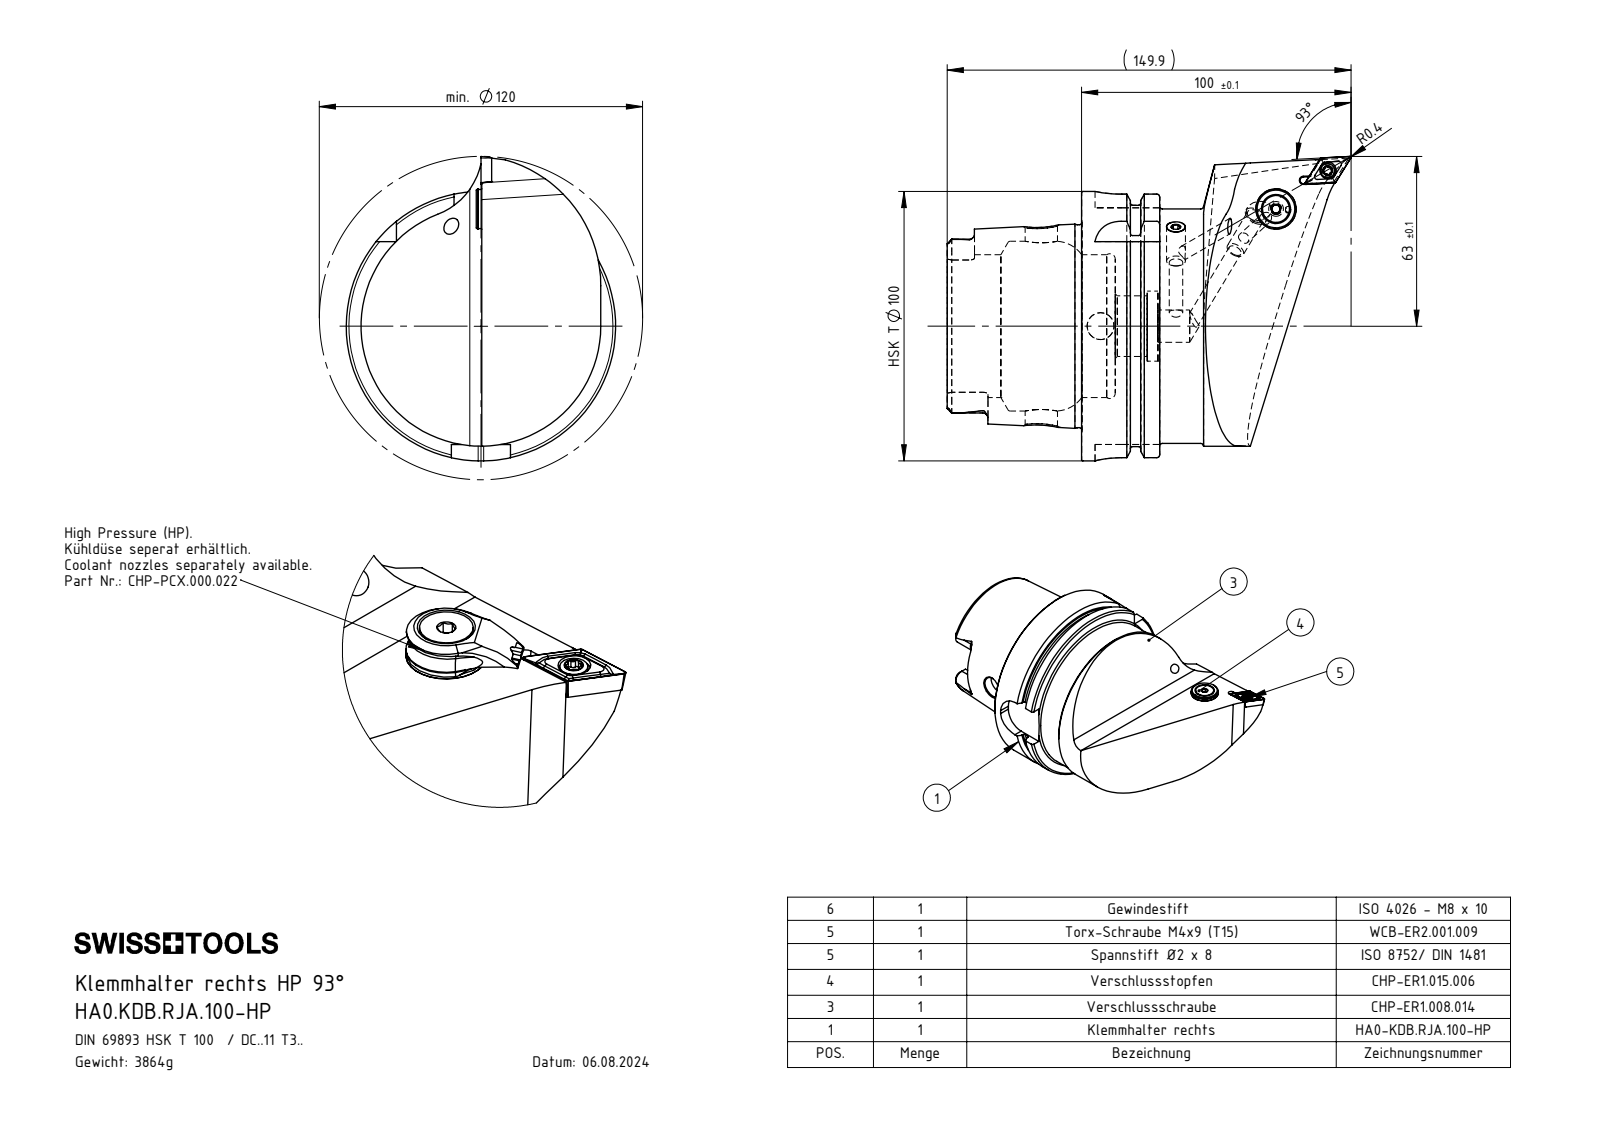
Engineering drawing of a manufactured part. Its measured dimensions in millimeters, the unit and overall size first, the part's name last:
Units: millimetres
Overall size (bounding box): 149.91 × 113 × 100
Round holes (diameter × count): ⌀5 ×3, ⌀4.2 ×2, ⌀12 ×2, ⌀1.2 ×1, ⌀2 ×1, ⌀2.5 ×1, ⌀3 ×1, ⌀3.3 ×1, ⌀4.4 ×1, ⌀5.2 ×1, ⌀6.1 ×1, ⌀6.8 ×1
Round bosses / shafts (diameter × count): ⌀8 ×2, ⌀100 ×1, ⌀91.95 ×1, ⌀87 ×1, ⌀75.26 ×1, ⌀15 ×1, ⌀13.4 ×1, ⌀10 ×1
Partial cylindrical surfaces — rounded edges, fillets, slot ends (radius × count): R0.34 ×6, R0.59 ×6, R1.9 ×6, R10 ×4, R4.83 ×2, R4.88 ×2, R1.25 ×1, R6 ×1
Main face-to-face distances: 12.45, 28.95, 16.5, 49.9, 62.35, 78.85, 87.8, 78.2, 28.3, 15.85
Hole centre spacings: 4.5, 20.7, 20.82, 23.9, 24.03, 78.34, 81.94, 102.22
Volume: 490 926 mm³ · Surface area: 69 738 mm²
Bodies: 9 solids, 427 faces (119 planar, 128 cylindrical, 180 other)
Part name (STEP PRODUCT): DIN 7991 - M5x15; HA0.KDB.RJA.100-HP; WCB-ER2.001.009_A; HA0-KDB.RJA.100-HP_A_Fertigbearbeitung (+7 more)
STEP written by: SolidWorks 2022 (AUTOMOTIVE_DESIGN)
